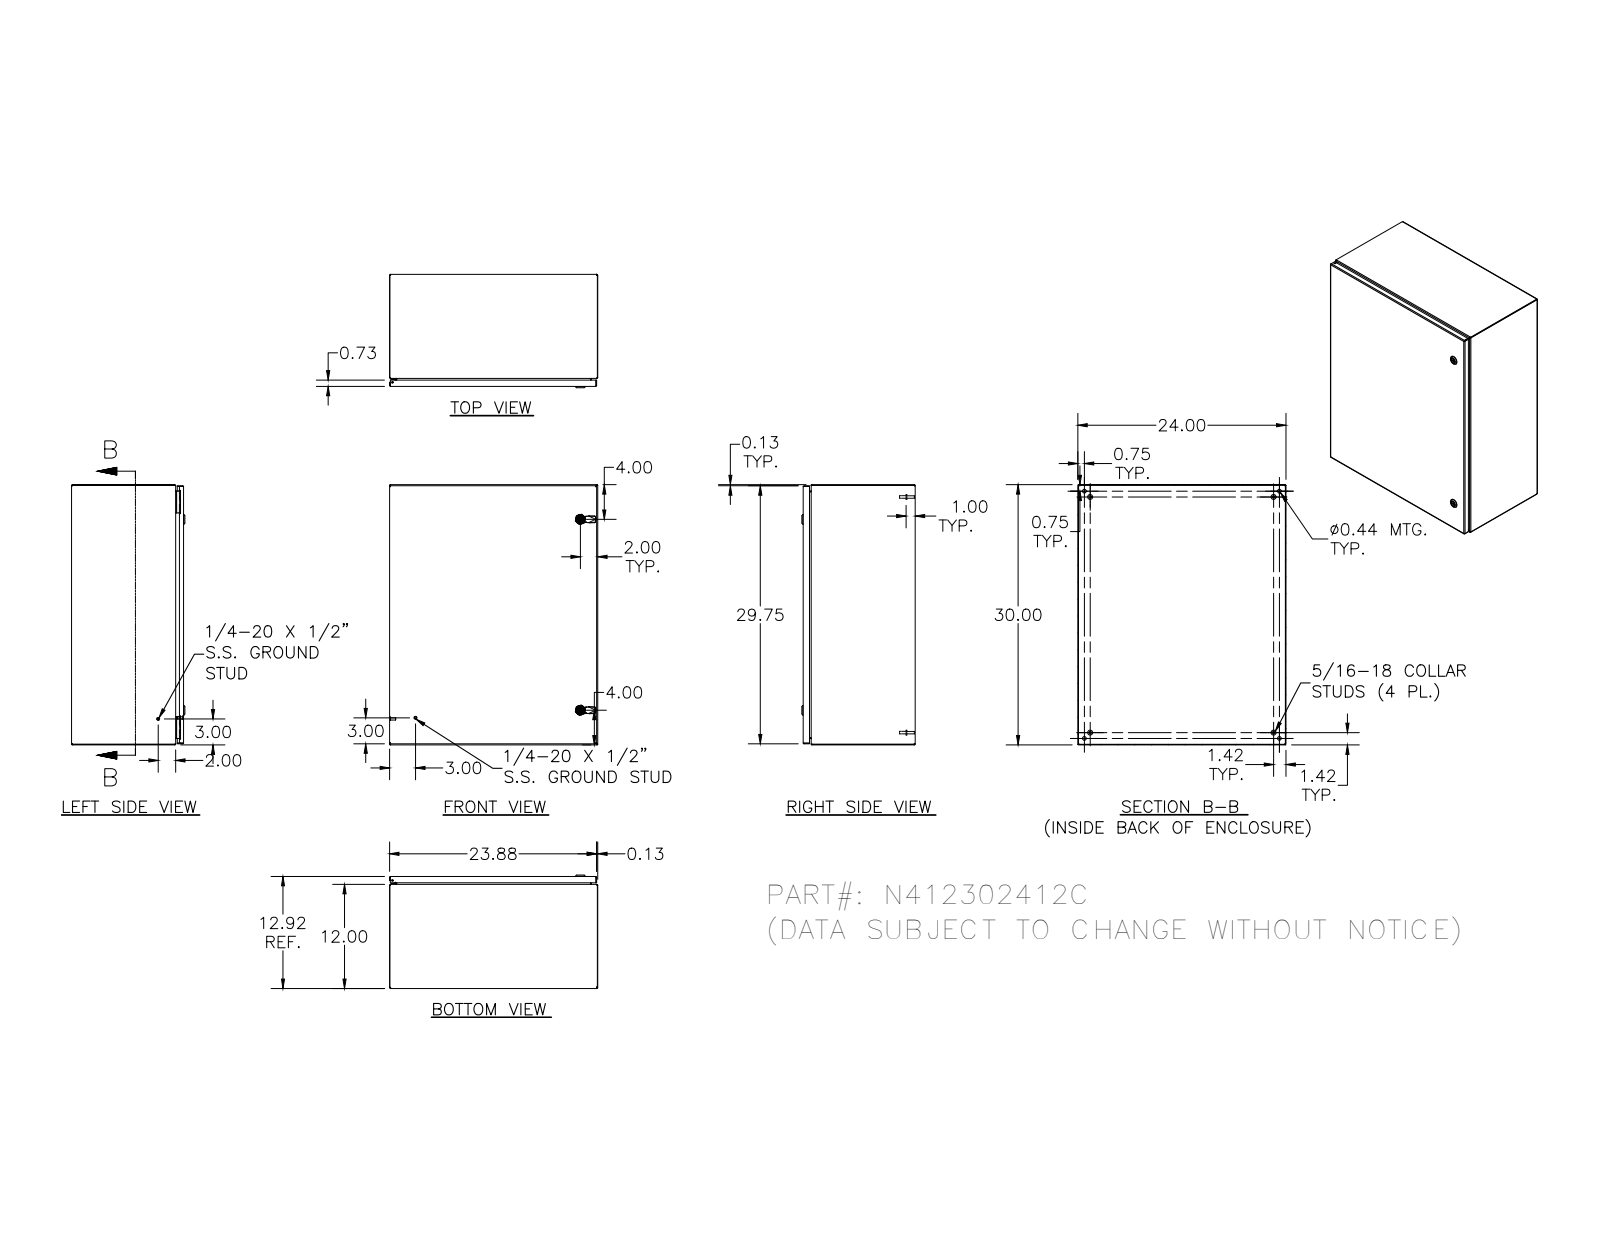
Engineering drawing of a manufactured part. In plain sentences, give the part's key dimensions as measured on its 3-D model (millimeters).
The part is named "N412302412C; N4123024CLID; 35124; 1000-u155_asm (+8 more)". Its 3-D file was written by "Autodesk Inventor 2011 (AUTOMOTIVE_DESIGN)". It is 38 solids with 1816 faces: 706 planar, 678 cylindrical and 432 other. Overall it measures 762 by 609.6 by 332.1 millimeters. Its volume is 3 576 000 cubic millimeters and its surface area 3 830 000 square millimeters. Round holes: 5 of diameter 4.8, 4 of diameter 2.4, 4 of diameter 3.9, 4 of diameter 4.2, 4 of diameter 4.4, 4 of diameter 11.1, 2 of diameter 4, 2 of diameter 5, 2 of diameter 8, 2 of diameter 10, 2 of diameter 10.2, 2 of diameter 16.1. Round bosses or shafts: 10 of diameter 6.4, 4 of diameter 14.3, 4 of diameter 9.1, 4 of diameter 8.1, 4 of diameter 7.6, 4 of diameter 7, 4 of diameter 6.5, 4 of diameter 4.2. Partial cylindrical surfaces (rounded edges, fillets, slot ends): 54 of radius 0.3, 30 of radius 0.8, 26 of radius 1.3, 23 of radius 0.5, 20 of radius 2.7, 18 of radius 0.4, 16 of radius 3.2, 8 of radius 0.8. The main face-to-face distances are 1.9, 326.2, 1.9, 324.3, 328.1, 760.1, 607.7, 605.8, 607.7, 609.6. The hole center spacings are 660.4, 16.8, 16.7, 33.2, 49.9, 12.7, 25, 33.3.
